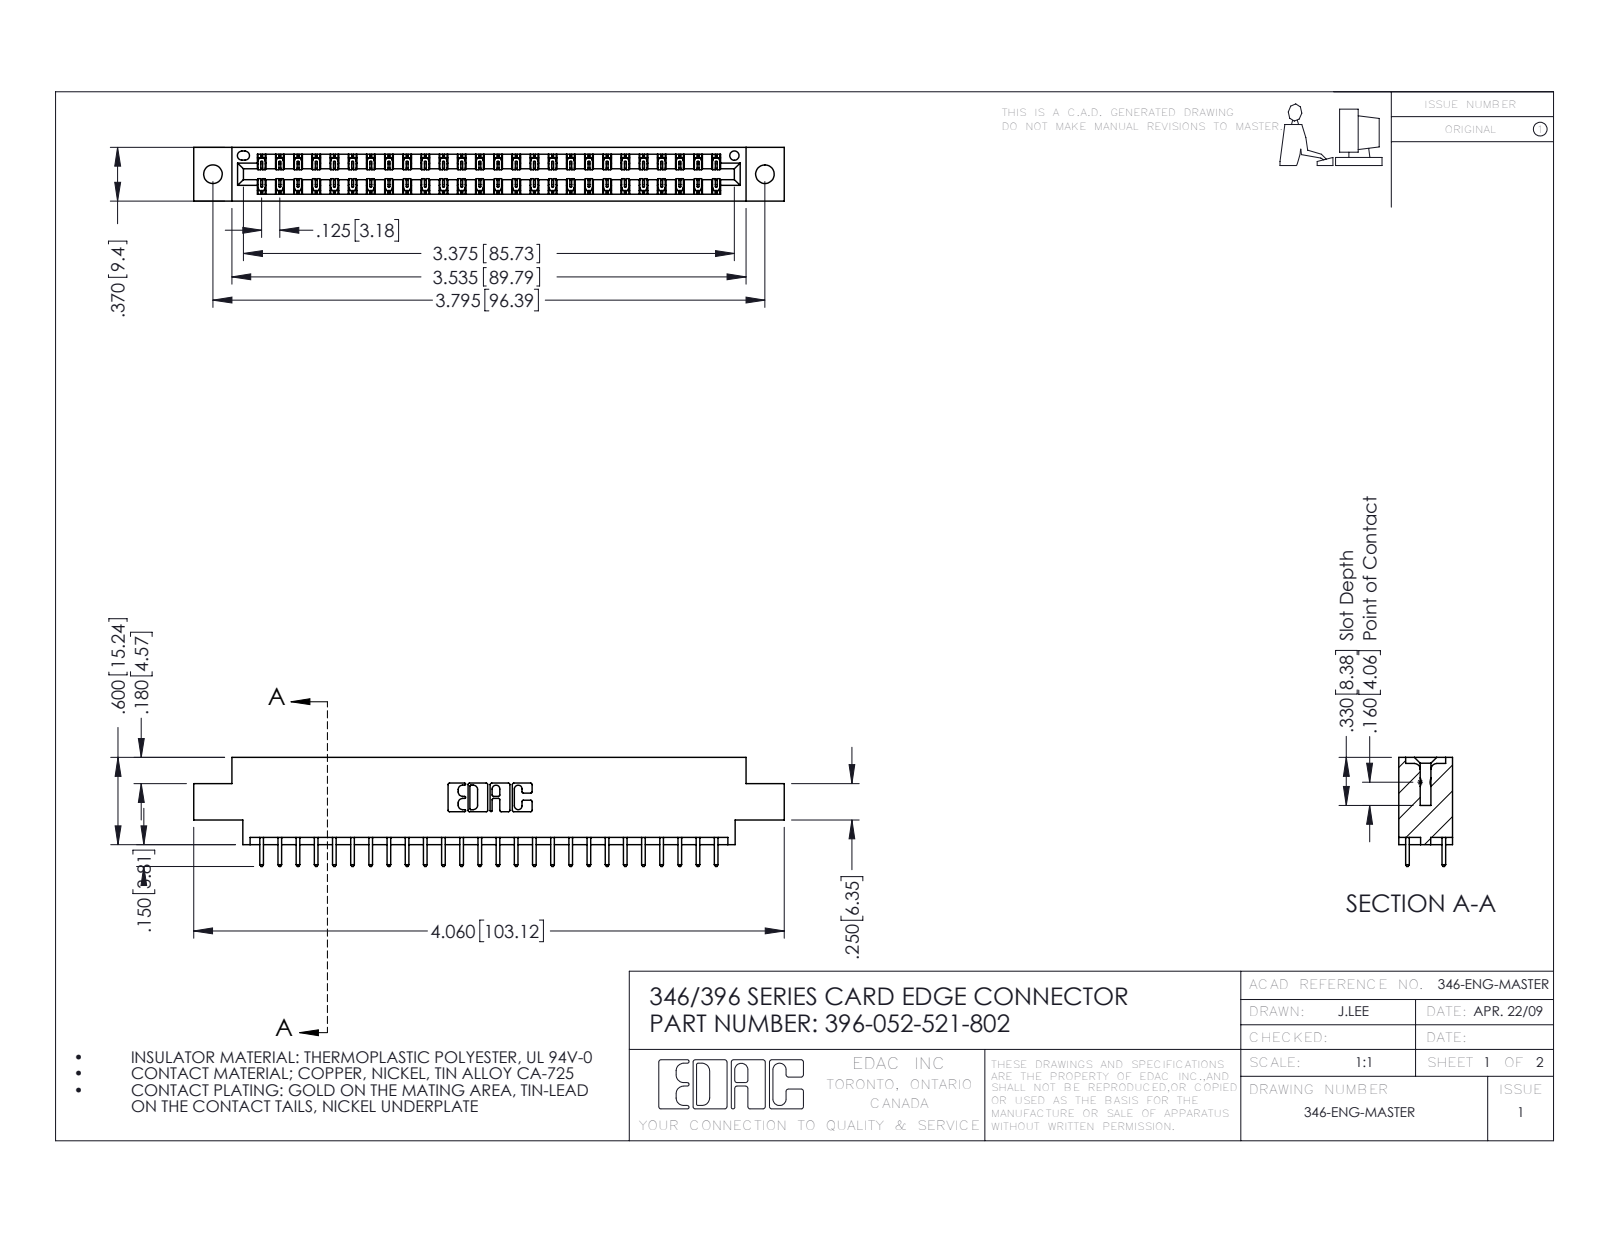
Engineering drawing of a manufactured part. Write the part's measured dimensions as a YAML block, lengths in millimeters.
part_name: "345-292-001_345-293-121; 346 Part_0.170 Offset - 0.128 Dia; 396-052-521-802"
step_written_by: "SolidWorks 2016 (CONFIG_CONTROL_DESIGN)"
units: millimeters
bodies: {solids: 53, faces: 2830, planar: 1900, cylindrical: 930, other: 0}
overall_size: [103.1, 19.1, 9.4]
volume: 9720
surface_area: 12880
round_holes:
  - {diameter: 3.3, count: 2}
  - {diameter: 1.6, count: 1}
partial_cylinders:
  - {radius: 0.2, count: 78}
  - {radius: 0.3, count: 52}
  - {radius: 0.3, count: 22}
  - {radius: 0.2, count: 6}
  - {radius: 0.8, count: 6}
  - {radius: 0.7, count: 3}
  - {radius: 0.4, count: 2}
  - {radius: 0.6, count: 2}
face_to_face_distances: [1.2, 8.2, 9.4, 6.4, 1.8, 7.6, 0.6, 7, 3.8, 5.6]
hole_center_spacings: [6.2, 91.1, 96.4]
